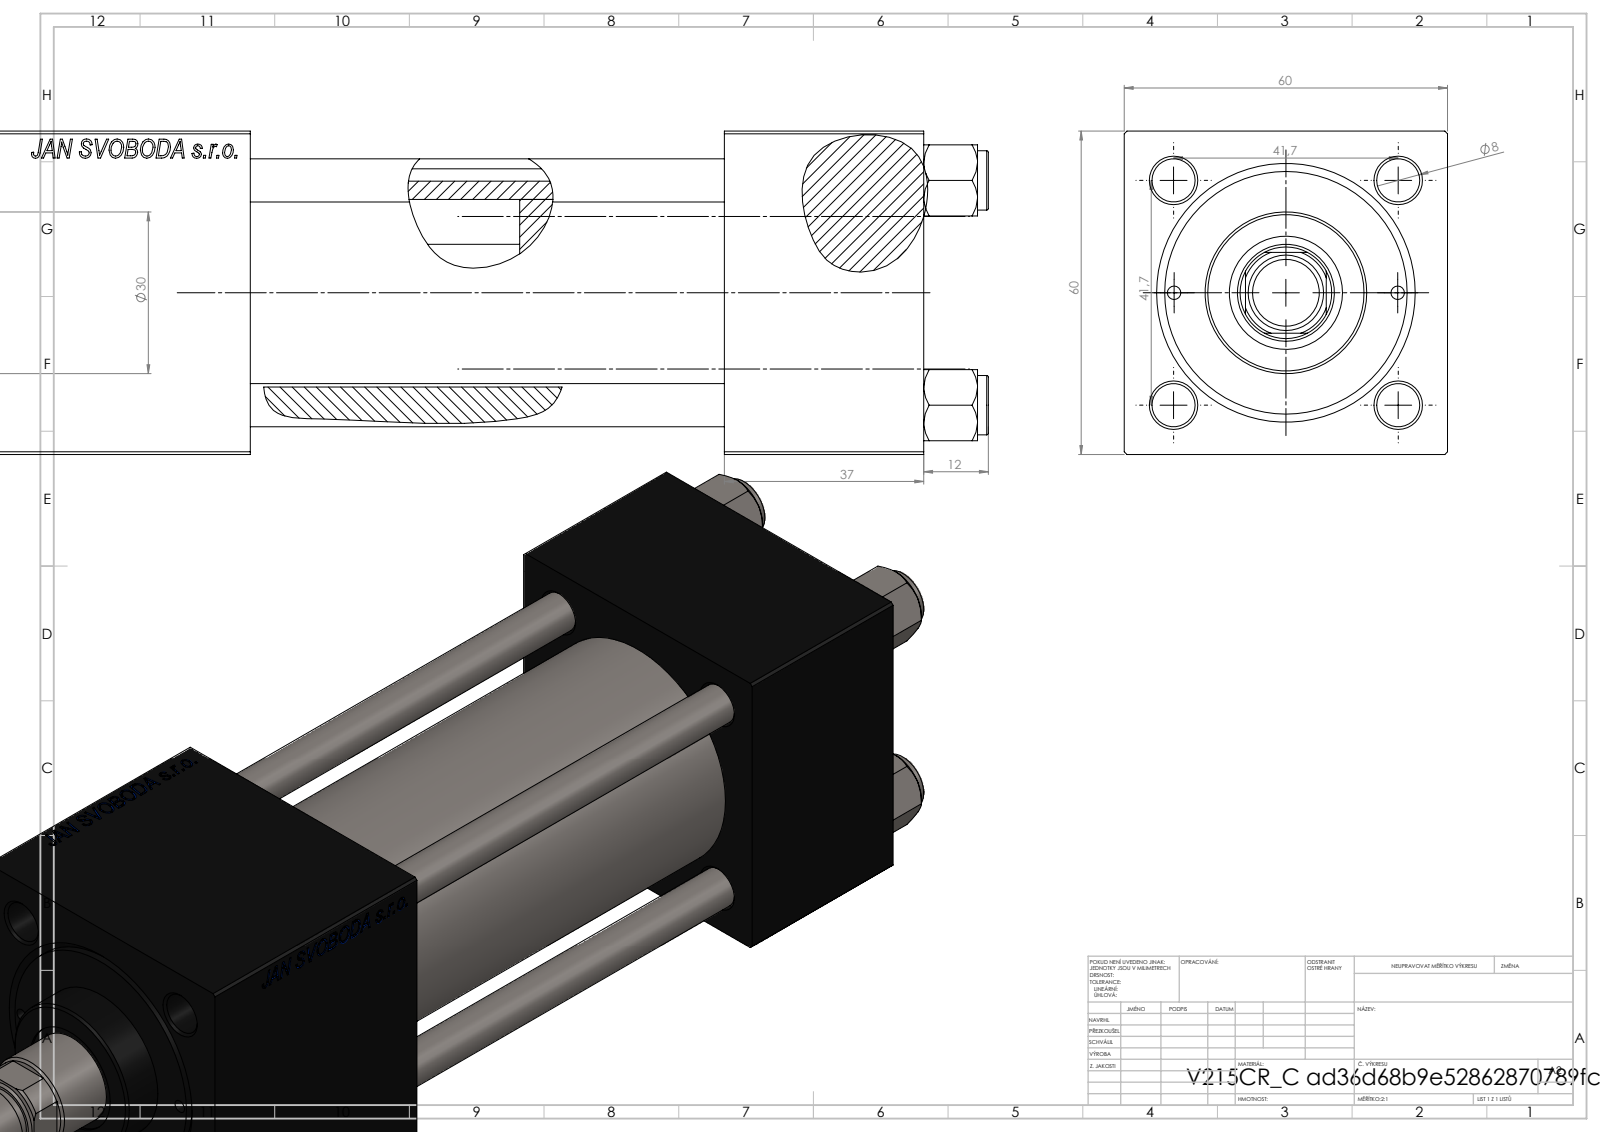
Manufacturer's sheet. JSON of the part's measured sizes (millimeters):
{"part_name": "V215_VC_A; ROD_END_AH; V215CR_C_TYCINKA; NUT_M5_C (+2 more)", "step_written_by": "SolidWorks 2019 (CONFIG_CONTROL_DESIGN)", "units": "millimeters", "bodies": {"solids": 12, "faces": 1168, "planar": 532, "cylindrical": 94, "other": 542}, "overall_size": [233, 60, 60], "volume_mm3": 431016, "surface_area_mm2": 119351, "round_holes": [[8, 4], [2.5, 2], [7, 2], [16.66, 2], [24, 2], [8.5, 1], [18, 1], [21, 1], [31, 1], [40, 1], [45, 1]], "round_bosses_or_shafts": [[11, 4], [46, 1], [30, 1], [14, 1], [12, 1]], "partial_cylinders_radius": [[8.5, 1]], "face_to_face_distances": [60, 37, 178, 141, 53, 125, 88, 149.3, 112.3, 24.3], "hole_center_spacings": [20.85, 29.49, 41.7, 46.53, 20.75, 58.97, 41.5, 122.5]}
